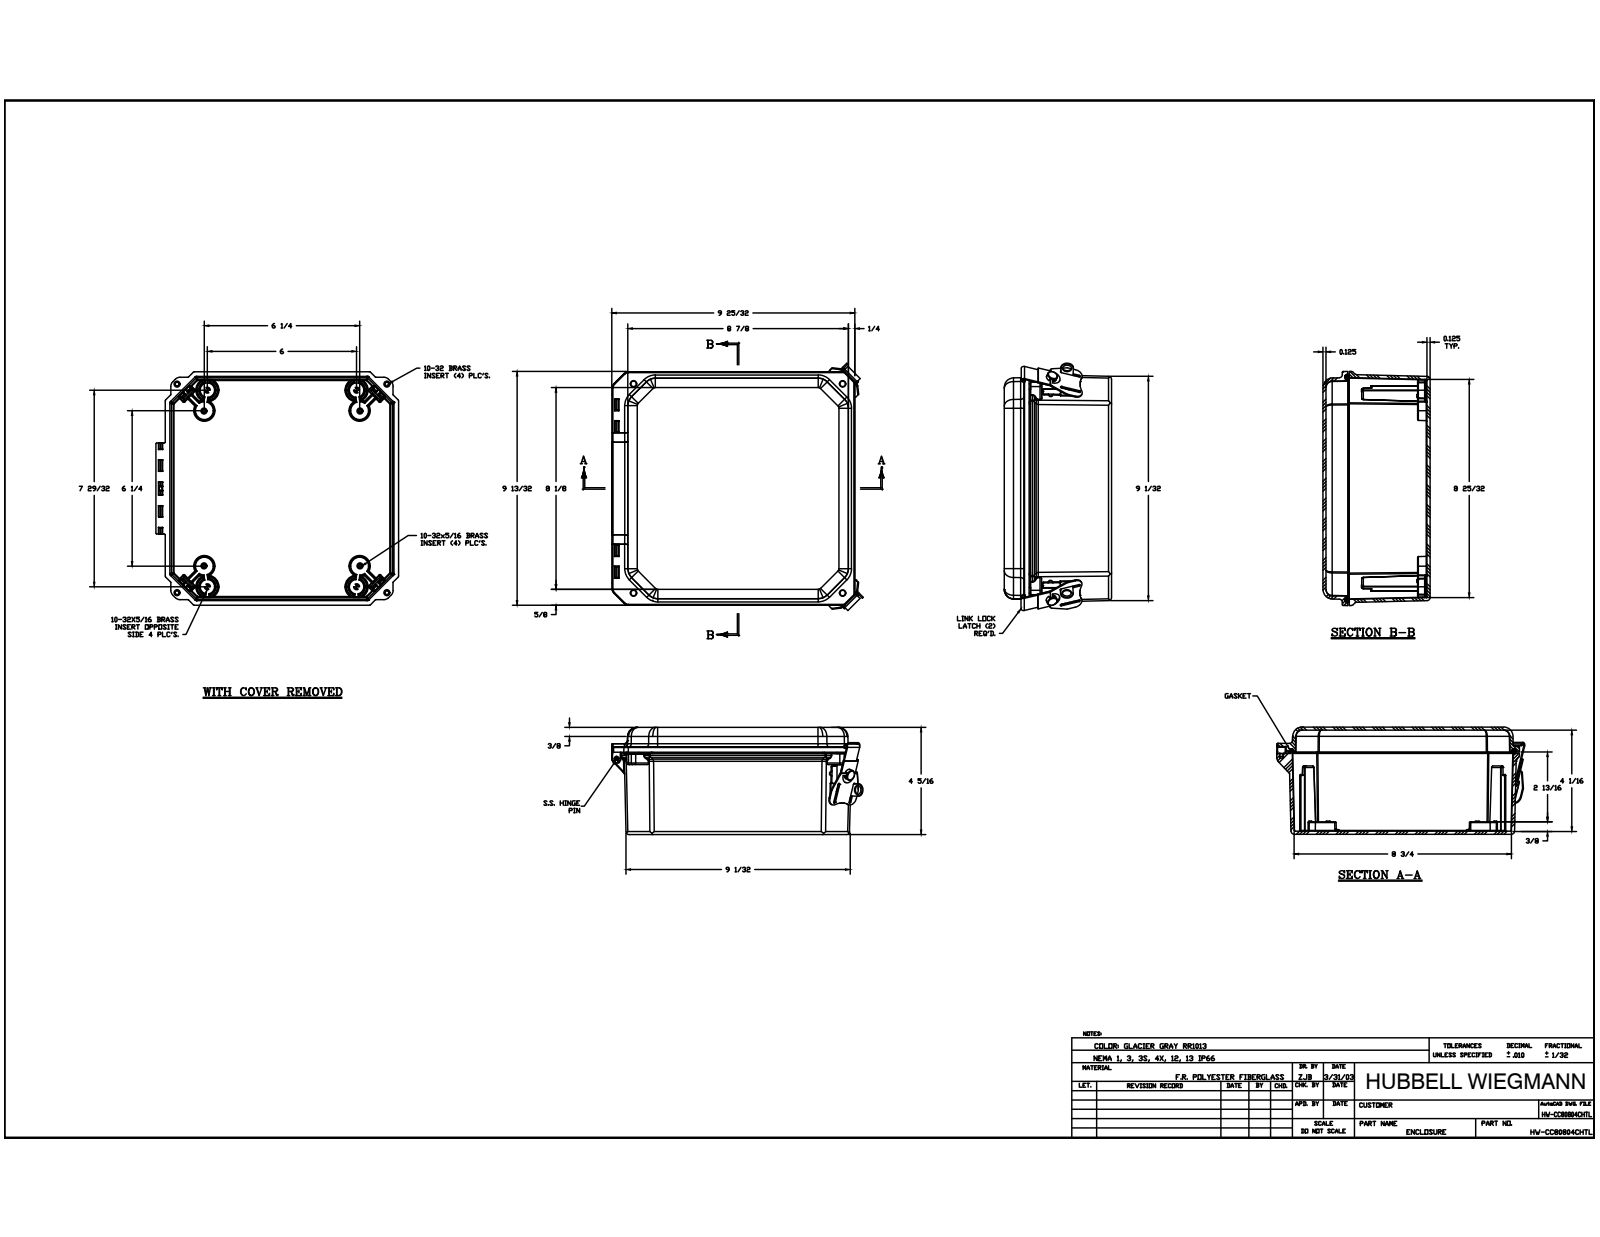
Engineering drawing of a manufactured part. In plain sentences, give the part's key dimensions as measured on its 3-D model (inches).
The part is named "DS080804BOX; DSCC080804CVR; GA808; WP808HLU (+6 more)". Its 3-D file was written by "Autodesk Inventor 2014 (AUTOMOTIVE_DESIGN)". It is 31 solids with 2217 faces: 646 planar, 853 cylindrical and 718 other. Overall it measures 10.263 by 10.202 by 4.312 inches. Its volume is 45.57 cubic inches and its surface area 716.9 square inches. Round holes: 12 of diameter 0.156, 8 of diameter 0.152, 4 of diameter 0.098, 4 of diameter 0.15, 4 of diameter 0.219, 4 of diameter 0.252, 4 of diameter 0.312, 2 of diameter 0.05, 2 of diameter 0.12, 2 of diameter 0.363, 1 of diameter 0.137. Round bosses or shafts: 12 of diameter 0.246, 4 of diameter 0.87, 4 of diameter 0.209, 4 of diameter 0.2, 3 of diameter 0.135, 3 of diameter 0.05, 2 of diameter 0.6. Partial cylindrical surfaces (rounded edges, fillets, slot ends): 160 of radius 0.01, 94 of radius 0.005, 67 of radius 0.02, 41 of radius 0.125, 38 of radius 0.03, 28 of radius 0.039, 26 of radius 0.25, 24 of radius 0.03. The main face-to-face distances are 0.125, 4.187, 4.312, 4.062, 0.124, 3.531, 0.656, 0.875, 3.312, 3.187. The hole center spacings are 6.25, 6.25, 7.411, 0.837, 6.181, 7.08, 7.411, 8.414.
